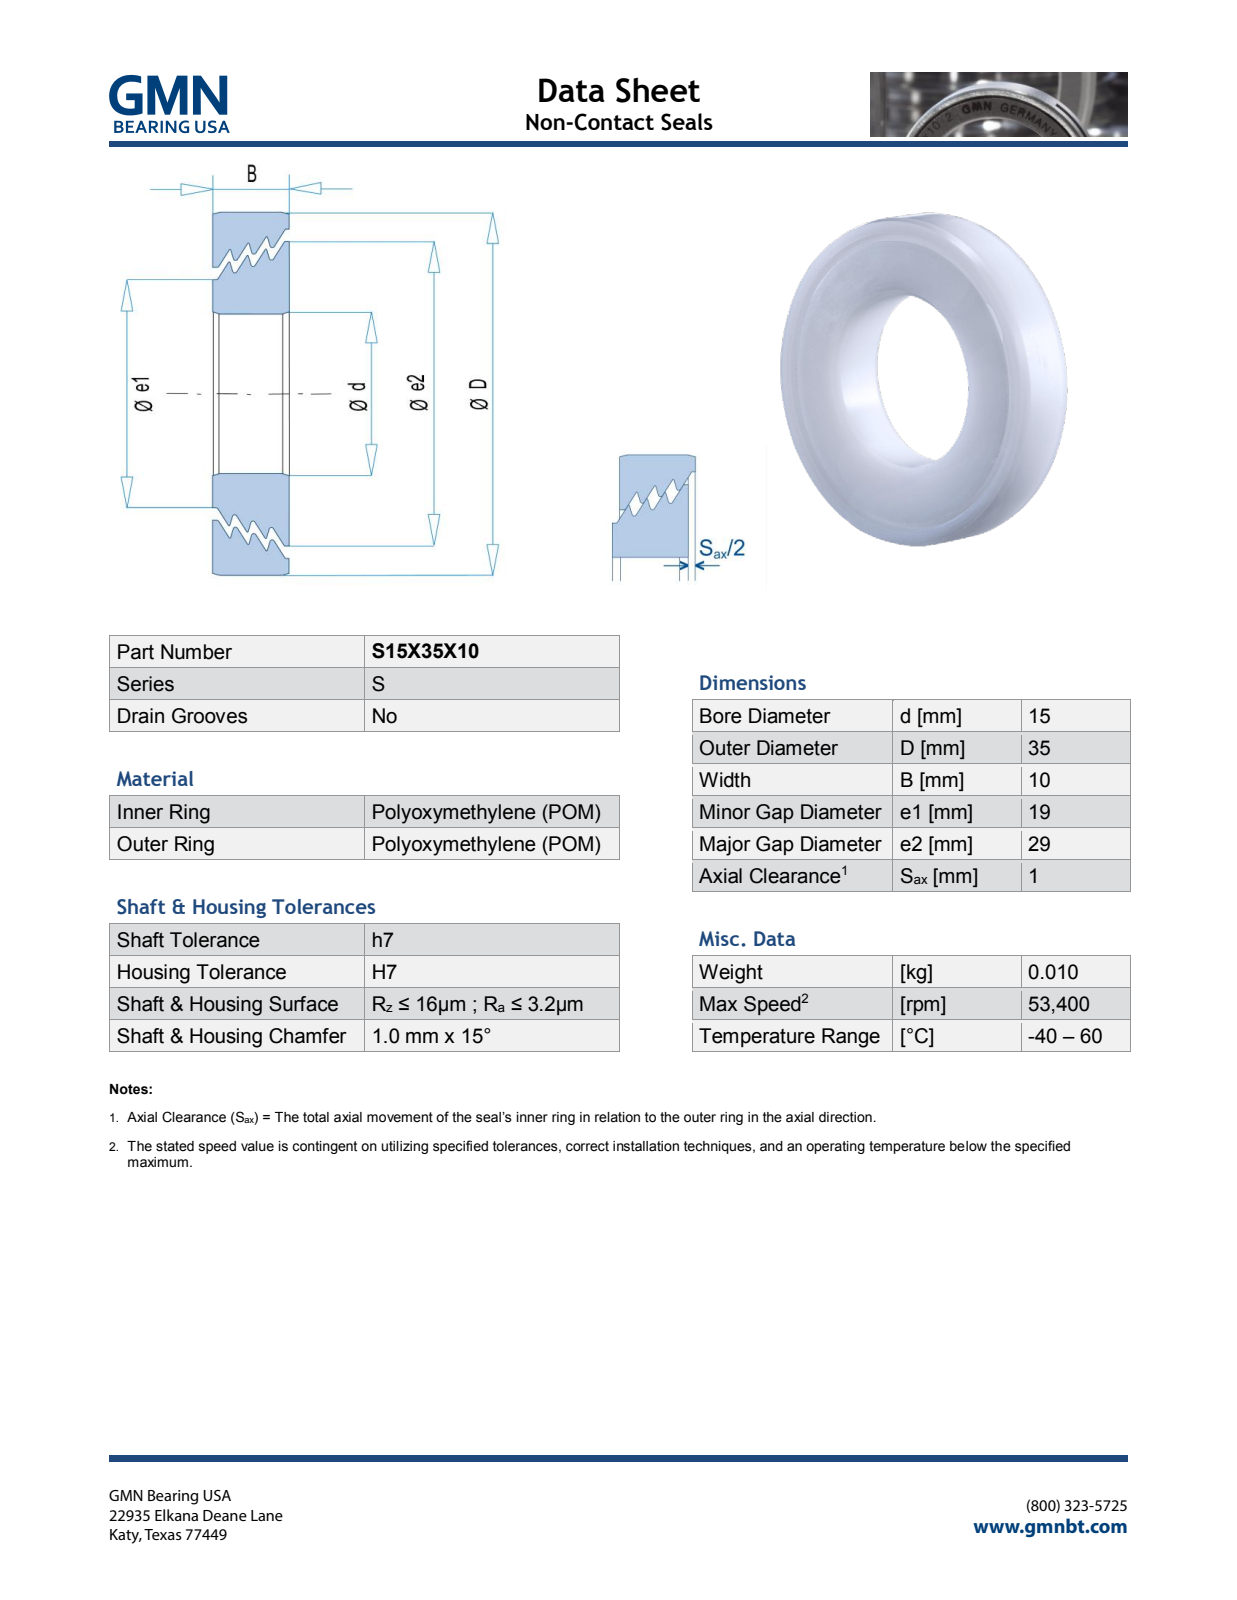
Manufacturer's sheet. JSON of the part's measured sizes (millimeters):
{"part_name": "S15X35X10_PRT", "step_written_by": "PRO/ENGINEER BY PARAMETRIC TECHNOLOGY CORPORATION, 2013150 (AUTOMOTIVE_DESIGN)", "units": "millimeters", "bodies": {"solids": 2, "faces": 641, "planar": 561, "cylindrical": 12, "other": 68}, "overall_size": [35, 35, 10.07], "volume_mm3": 7177, "surface_area_mm2": 6170, "round_holes": [[15, 1], [20.63, 1], [30.63, 1]], "round_bosses_or_shafts": [[35, 1], [29, 1], [19, 1]], "face_to_face_distances": [10, 10.07, 1.83, 1.6, 1.3, 1.37, 0.82, 1.53, 0.78, 1.07]}
